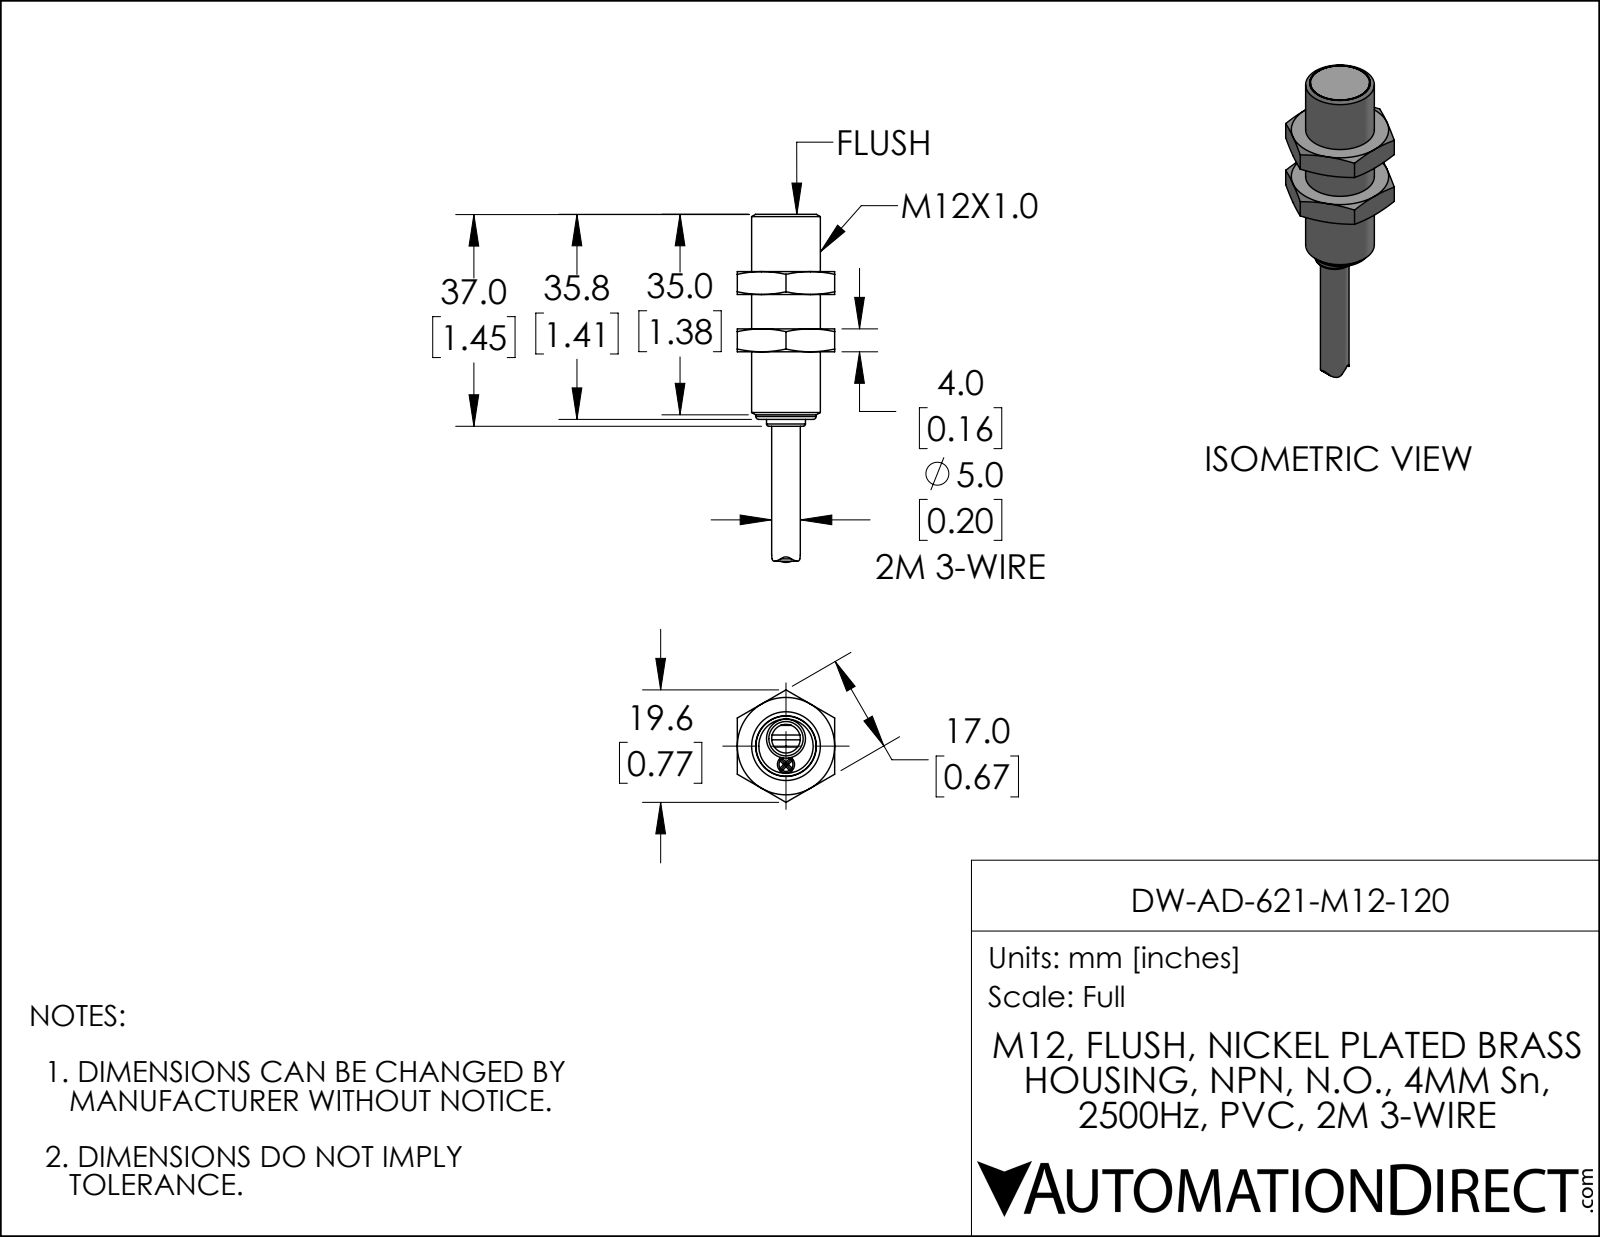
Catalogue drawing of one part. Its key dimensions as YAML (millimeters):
part_name: "DW-AD-621-M12-120"
step_written_by: "SolidWorks 2019 (AUTOMOTIVE_DESIGN)"
units: millimeters
bodies: {solids: 1, faces: 81, planar: 34, cylindrical: 14, other: 33}
overall_size: [60.8, 19.6, 17]
volume: 5600
surface_area: 2627
round_holes:
  - {diameter: 10.5, count: 1}
round_bosses_or_shafts:
  - {diameter: 12, count: 1}
  - {diameter: 10.5, count: 1}
  - {diameter: 10.3, count: 1}
  - {diameter: 6.8, count: 1}
  - {diameter: 5, count: 1}
  - {diameter: 3, count: 1}
partial_cylinders:
  - {radius: 0.8, count: 1}
  - {radius: 1, count: 1}
  - {radius: 4.2, count: 1}
  - {radius: 6.3, count: 1}
  - {radius: 8.4, count: 1}
face_to_face_distances: [10, 4, 17, 14, 6, 20, 24, 35.8, 25.8, 21.8]
